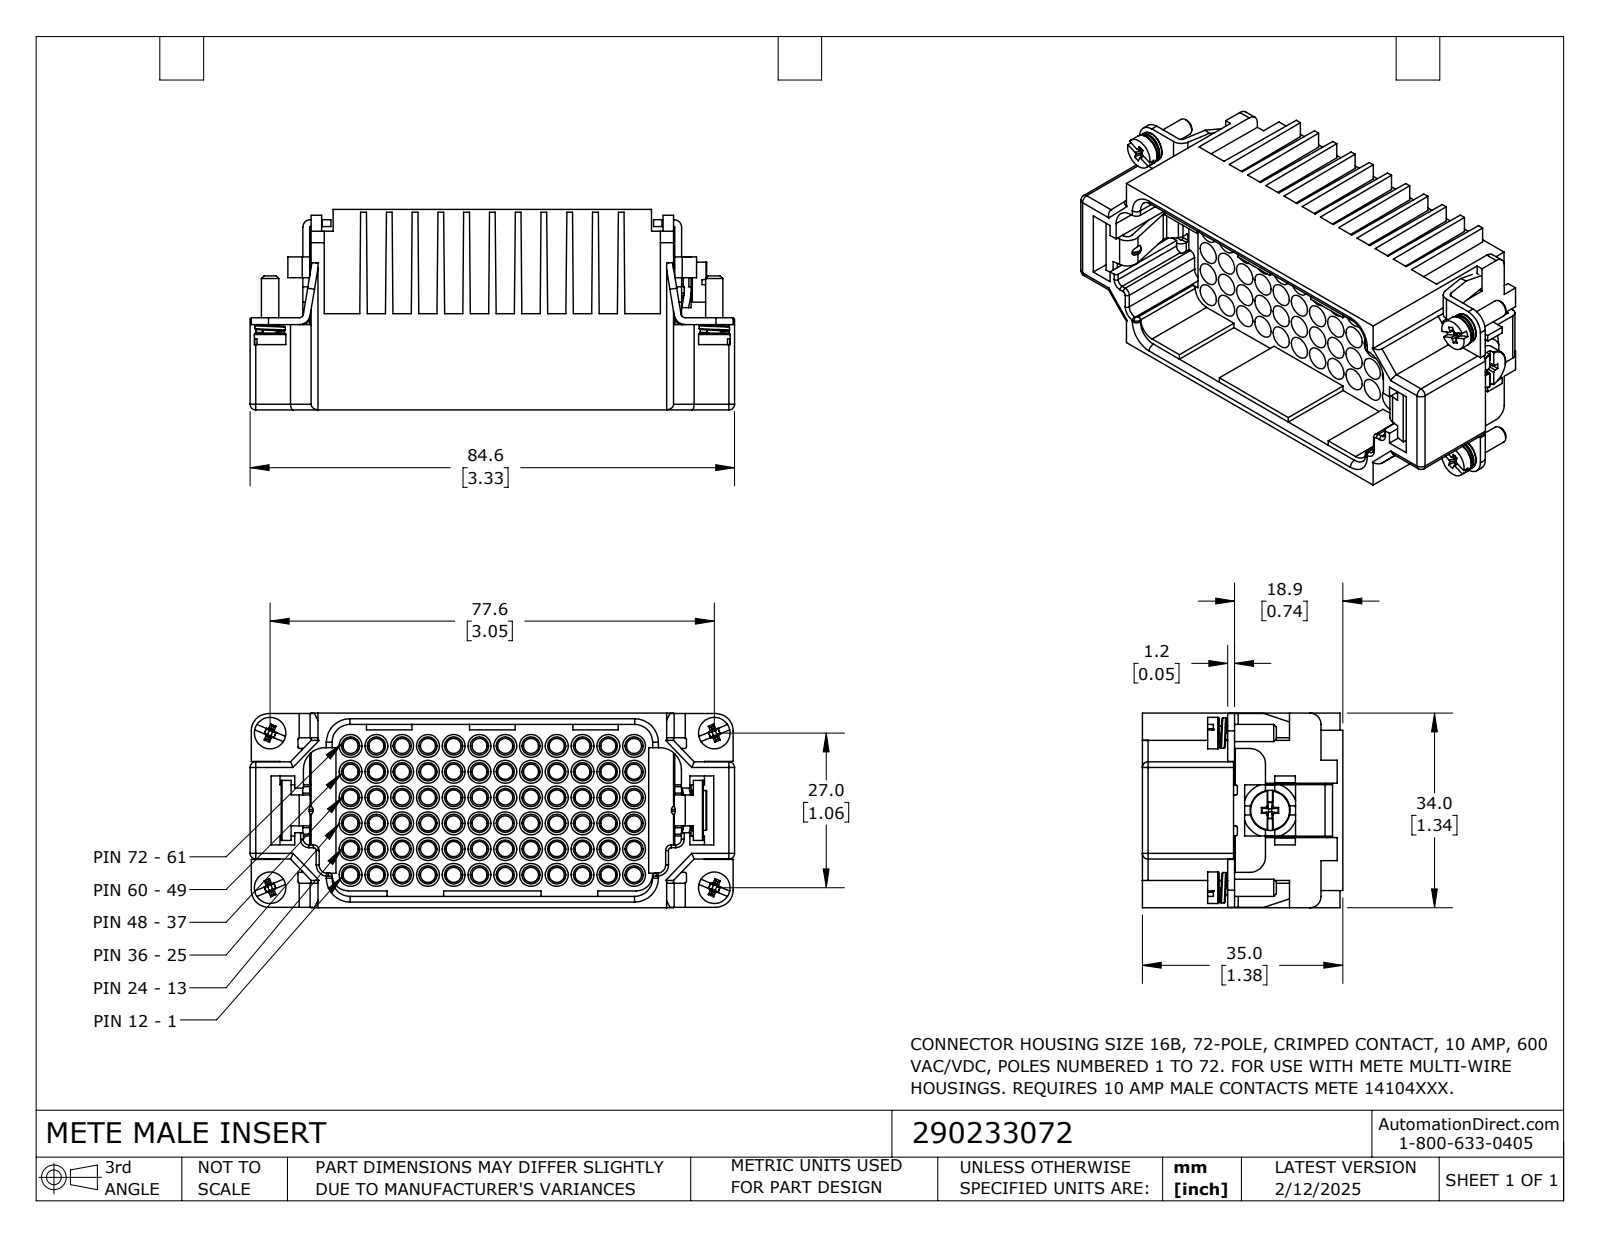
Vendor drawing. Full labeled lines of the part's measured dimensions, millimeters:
Part name (STEP PRODUCT): 290233072
STEP written by: SolidWorks 2024 (CONFIG_CONTROL_DESIGN)
Units: millimetres
Bodies: 13 solids, 1879 faces (842 planar, 948 cylindrical, 89 other)
Overall size (bounding box): 84.6 × 35 × 34
Volume: 31 640 mm³ · Surface area: 39 320 mm²
Round holes (diameter × count): ⌀2.6 ×72, ⌀3.2 ×72, ⌀4 ×72, ⌀2.9 ×4, ⌀3.3 ×1
Round bosses / shafts (diameter × count): ⌀5.5 ×4, ⌀5.3 ×4, ⌀3 ×4, ⌀2.4 ×4, ⌀7 ×1, ⌀5.1 ×1, ⌀3.9 ×1
Partial cylindrical surfaces — rounded edges, fillets, slot ends (radius × count): R0.3 ×32, R1 ×18, R0.5 ×15, R0.3 ×12, R0.1 ×10, R1.3 ×10, R0.2 ×8, R1.4 ×8
Main face-to-face distances: 4.5, 9, 13.5, 3, 31, 1.2, 22.5, 18, 27, 2
Hole centre spacings: 4.5, 10.1, 6.4, 9, 14.2, 18.5, 13.5, 23
